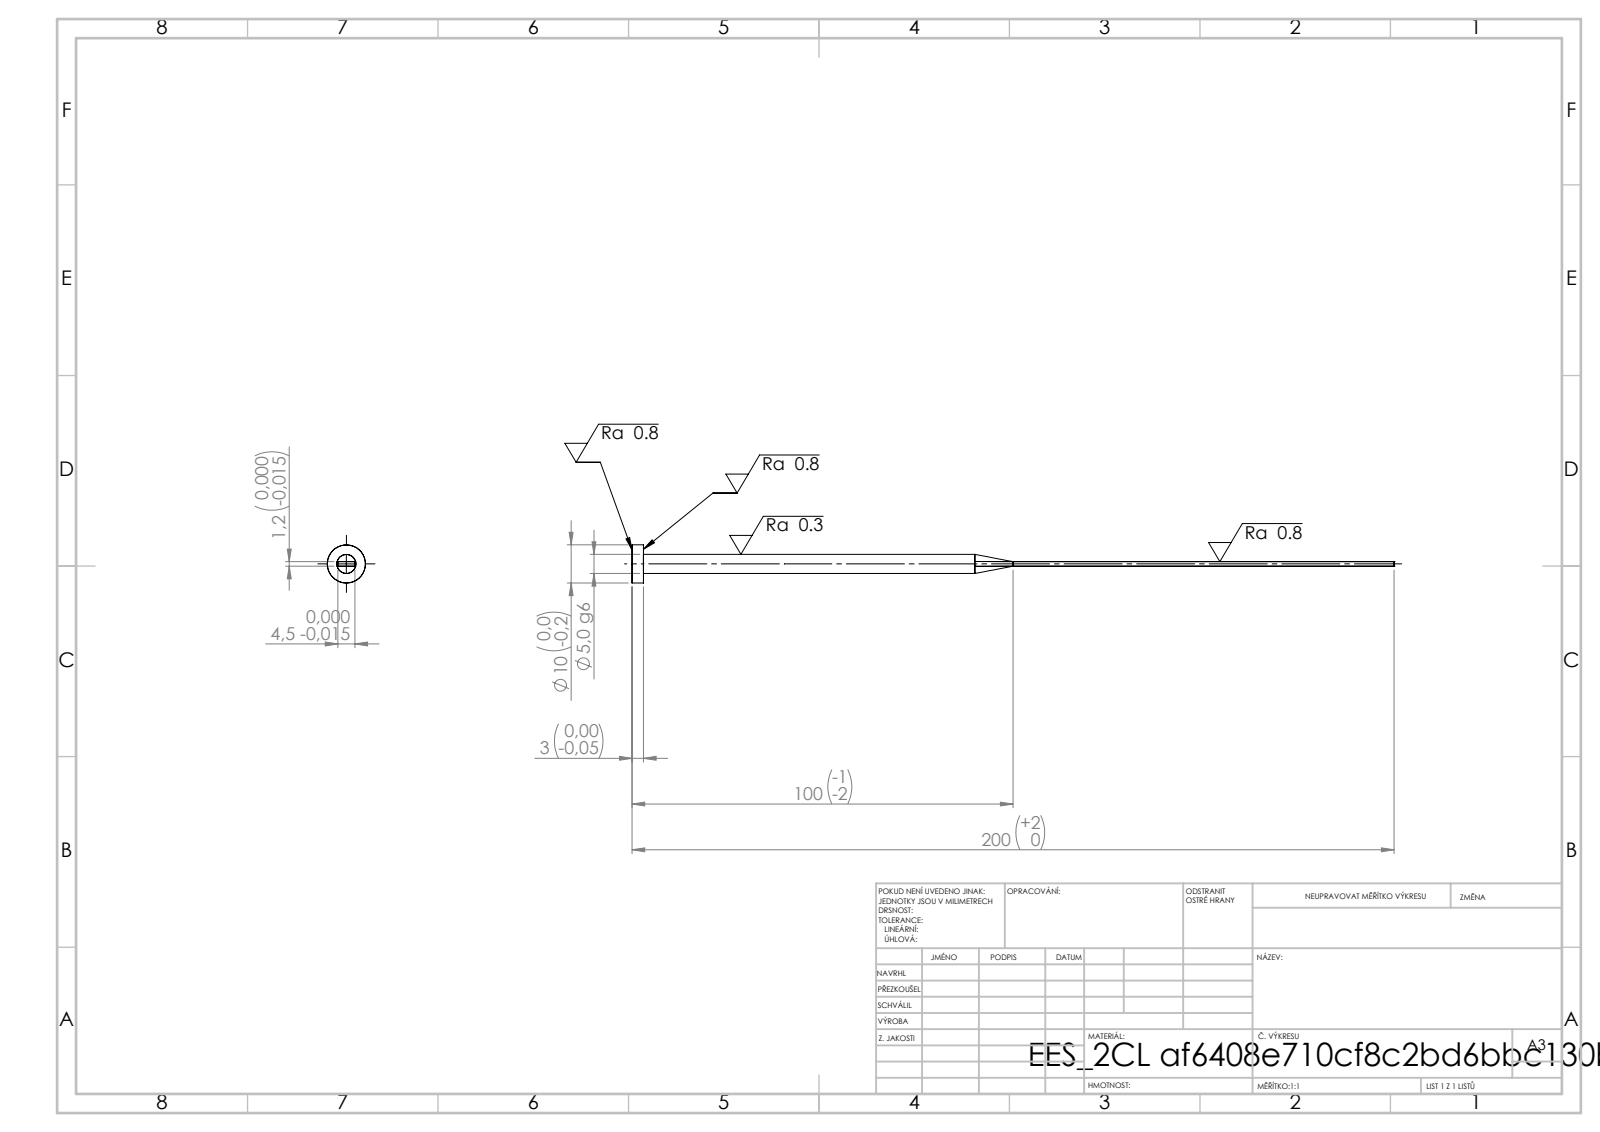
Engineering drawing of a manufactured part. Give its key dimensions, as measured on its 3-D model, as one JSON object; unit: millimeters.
{"step_written_by": "SolidWorks 2019 (CONFIG_CONTROL_DESIGN)", "units": "millimeters", "bodies": {"solids": 1, "faces": 15, "planar": 7, "cylindrical": 4, "other": 4}, "overall_size": [200, 10, 10], "volume_mm3": 2604, "surface_area_mm2": 2875, "round_bosses_or_shafts": [[10, 1], [5, 1]], "face_to_face_distances": [1.2, 4.5, 3, 200, 197]}
